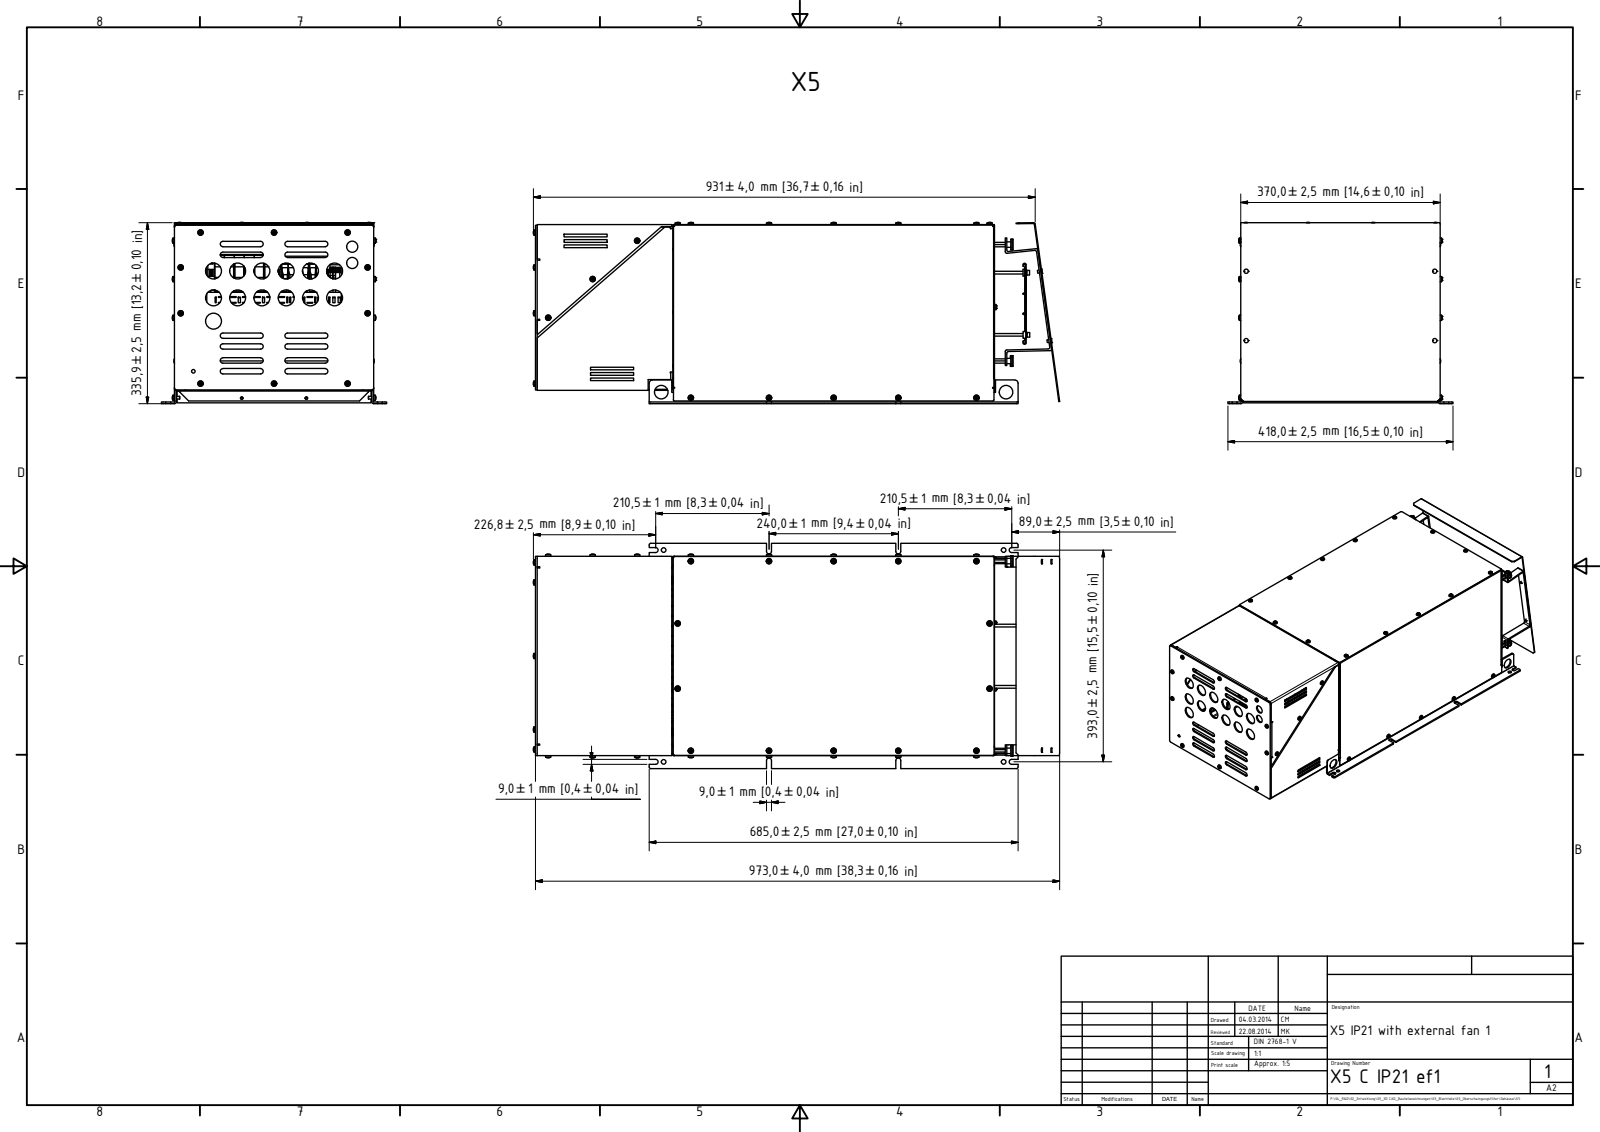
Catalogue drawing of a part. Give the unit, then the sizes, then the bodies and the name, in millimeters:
Units: millimetres
Overall size (bounding box): 976.82 × 418 × 336.32
Round holes (diameter × count): ⌀4.13 ×42, ⌀6.5 ×32, ⌀6.8 ×14, ⌀4 ×13, ⌀5.5 ×13, ⌀29.5 ×13, ⌀6 ×11, ⌀7 ×11, ⌀9 ×8, ⌀3.24 ×7, ⌀8.5 ×6, ⌀11 ×6
Round bosses / shafts (diameter × count): ⌀5 ×44, ⌀4.6 ×42, ⌀1.4 ×8, ⌀4 ×7, ⌀10 ×6, ⌀8 ×6, ⌀8.5 ×5, ⌀20 ×4
Partial cylindrical surfaces — rounded edges, fillets, slot ends (radius × count): R0.23 ×112, R0.5 ×76, R1 ×70, R2 ×63, R0.15 ×56, R0.1 ×41, R0.1 ×37, R5 ×31
Main face-to-face distances: 1, 2, 369, 368, 3, 370, 1.5, 305.75, 367, 309
Hole centre spacings: 120, 21, 350, 352, 36.37, 145, 265, 385
Volume: 3 765 000 mm³ · Surface area: 4 032 000 mm²
Bodies: 141 solids, 9074 faces (5291 planar, 2238 cylindrical, 1545 other)
Part name (STEP PRODUCT): 10100398 Deckel X5_X6; 10100399 Seitenwand X5; 10100396 Anschlussblech X5; 10100397 Lüfterblech X5 (+8 more)
STEP written by: Autodesk Inventor 2015 (AUTOMOTIVE_DESIGN)
